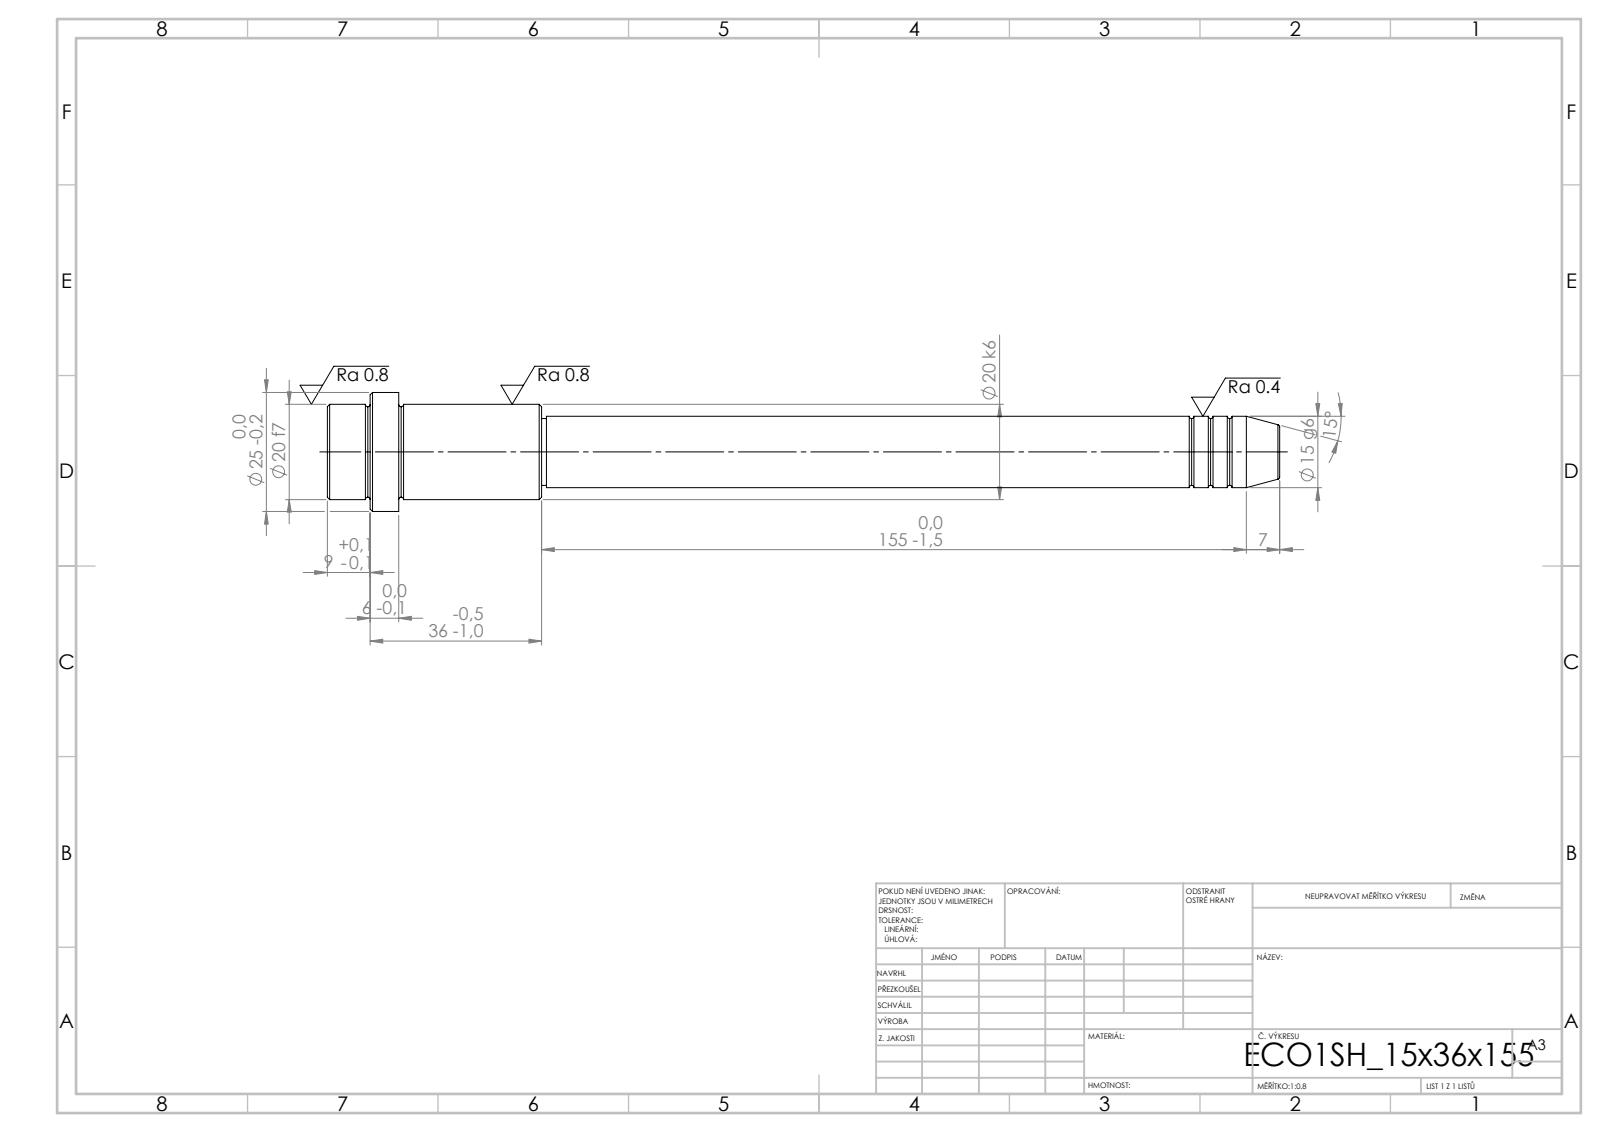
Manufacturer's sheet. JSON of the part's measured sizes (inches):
{"step_written_by": "SolidWorks 2019 (CONFIG_CONTROL_DESIGN)", "units": "inches", "bodies": {"solids": 1, "faces": 52, "planar": 6, "cylindrical": 16, "other": 30}, "overall_size": [7.874, 0.984, 0.984], "volume_in3": 2.572, "surface_area_in2": 17.38, "round_bosses_or_shafts": [[0.984, 1], [0.787, 1], [0.591, 1], [0.551, 1]], "face_to_face_distances": [0.591, 0.236, 0.354, 1.181, 1.417, 1.772, 6.102, 7.283, 7.52, 7.874]}
